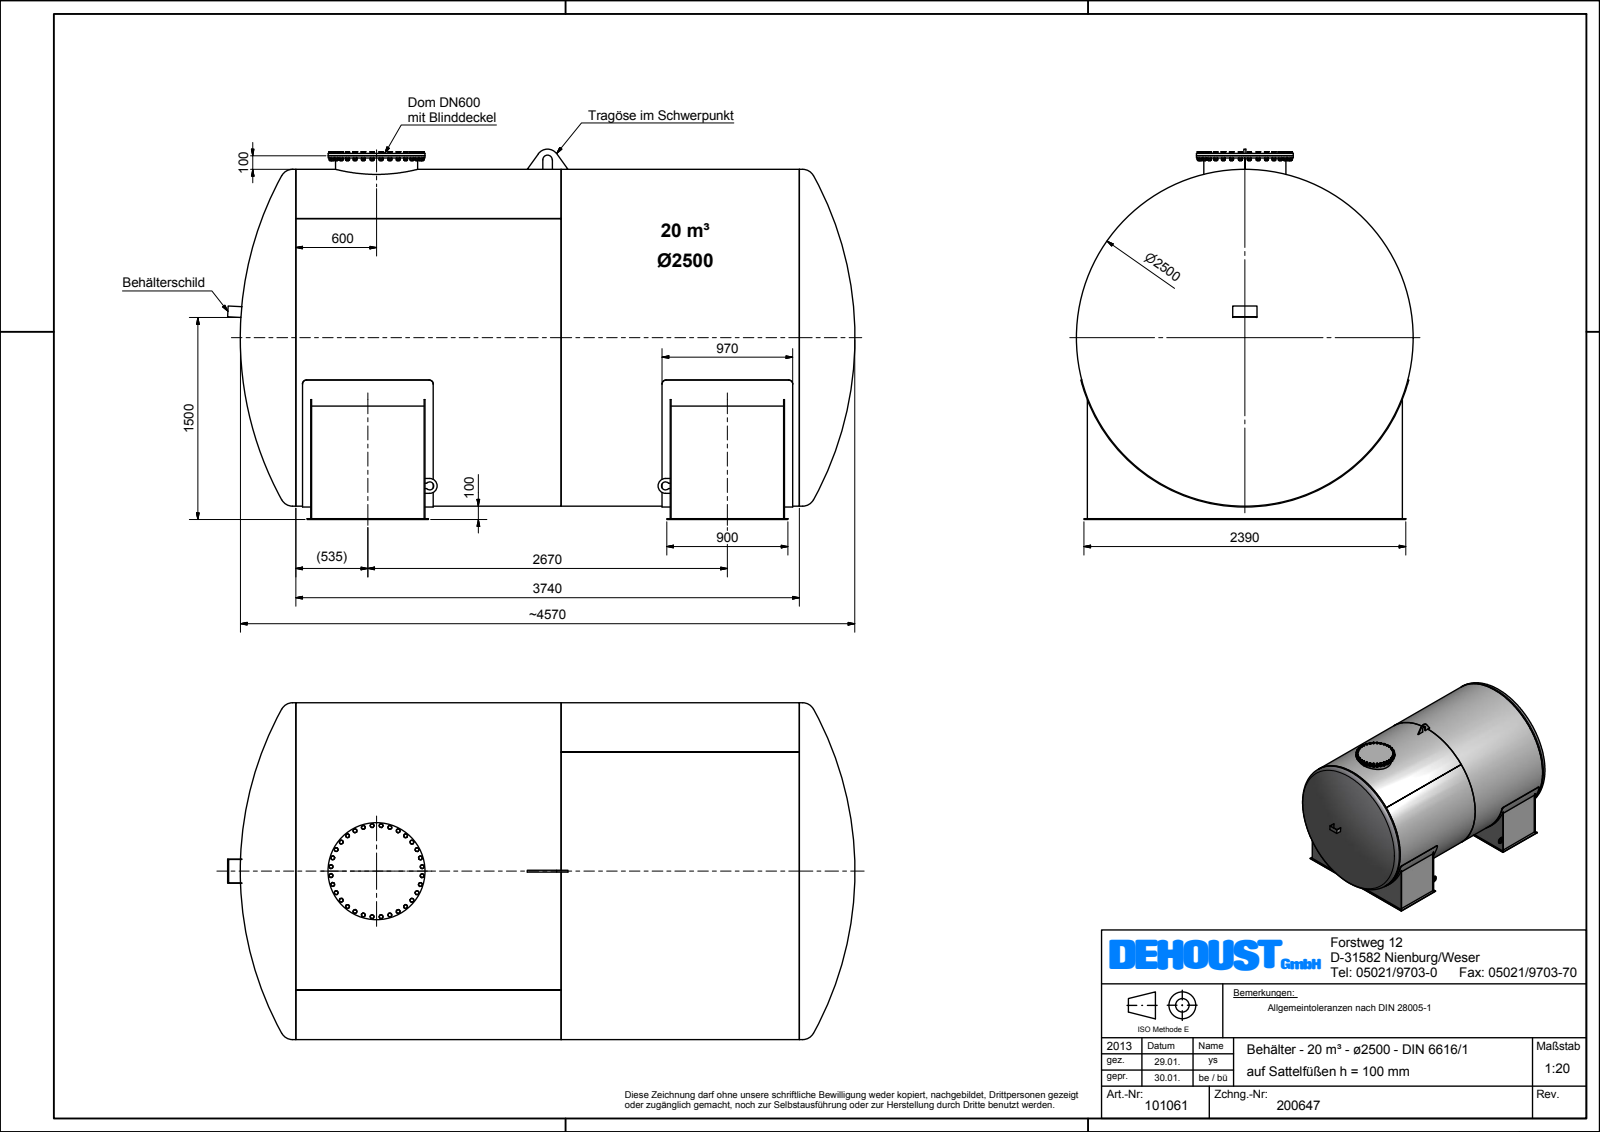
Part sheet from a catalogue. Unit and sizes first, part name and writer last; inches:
Units: inches
Overall size (bounding box): 183.379 × 108.268 × 98.425
Round holes (diameter × count): ⌀23.543 ×1, ⌀97.874 ×1
Round bosses / shafts (diameter × count): ⌀0.976 ×32, ⌀0.709 ×32, ⌀0.656 ×32, ⌀98.425 ×1, ⌀28.346 ×1, ⌀25.984 ×1, ⌀24.016 ×1
Partial cylindrical surfaces — rounded edges, fillets, slot ends (radius × count): R1.181 ×8, R1.17 ×2, R2.165 ×2, R1.378 ×1, R3.346 ×1, R49.488 ×1
Main face-to-face distances: 0.276, 147.244, 105.118, 33.15, 90.276, 105.394, 4.35, 142.894, 37.776, 109.469
Volume: 168 800 in³ · Surface area: 157 300 in²
Bodies: 3 solids, 1109 faces (656 planar, 161 cylindrical, 292 other)
Part name (STEP PRODUCT): Beh\S\dlter_6616_E_2500_020_100_KV
STEP written by: Autodesk Inventor 2012 (AUTOMOTIVE_DESIGN)
